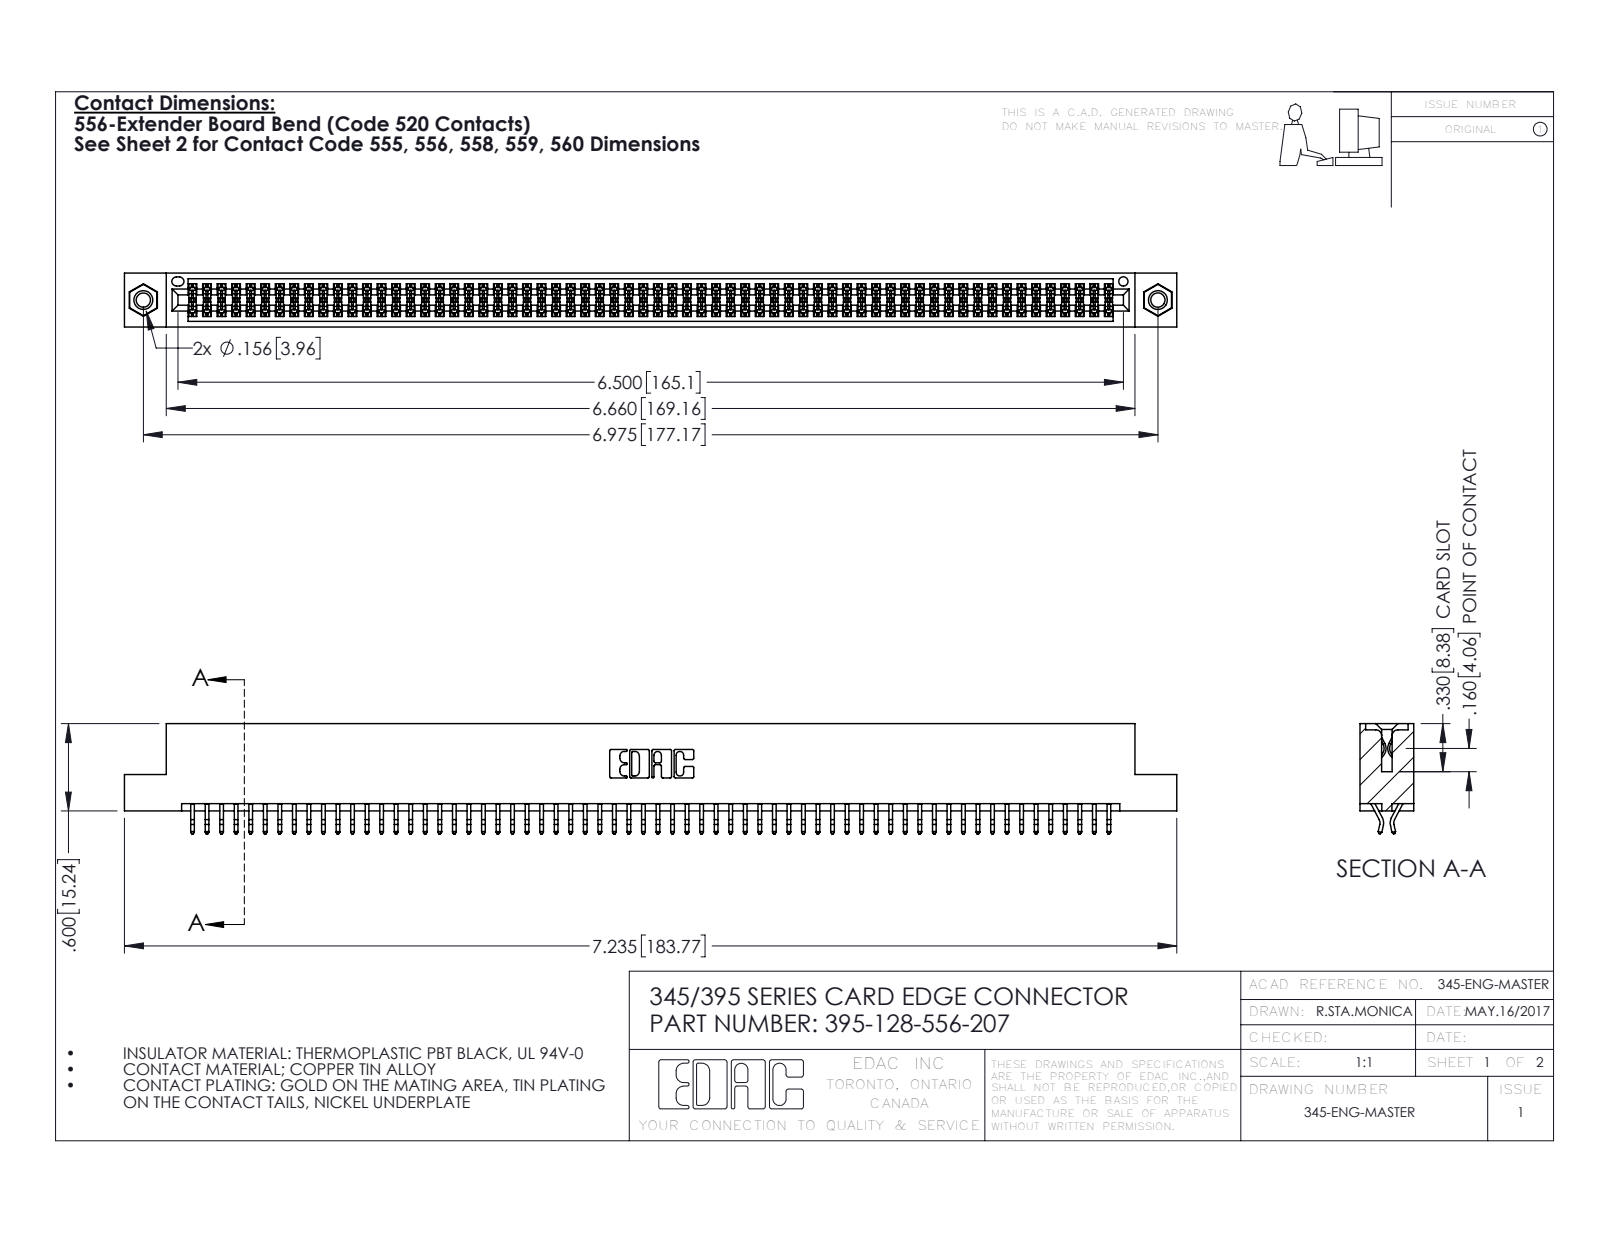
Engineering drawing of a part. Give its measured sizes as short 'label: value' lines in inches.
name: 395-128-556-207; 345-250-001_345-250-005-103; 345 Part_Flush Mounting Lugs - 0.156 Dia-TI; 345-292-001_556 Tail
written by: SolidWorks 2016 (CONFIG_CONTROL_DESIGN)
unit: in
bodies: 131 solids, 7354 faces (4848 planar, 2490 cylindrical, 16 other)
size: 7.235 × 0.757 × 0.37
volume: 1.101 in³; area: 41.86 in²
holes: 2× ⌀0.098, 2× ⌀0.125, 2× ⌀0.156, 1× ⌀0.064
bosses: 2× ⌀0.155
rounds: 192× R0.006, 22× R0.01, 6× R0.007, 6× R0.031, 3× R0.026, 2× R0.01, 2× R0.014, 2× R0.019
face distances: 0.072, 0.298, 0.37, 0.2, 0.025, 0.098, 0.272, 0.225, 0.175, 0.149
hole spacings: 0.27, 6.739, 6.975
